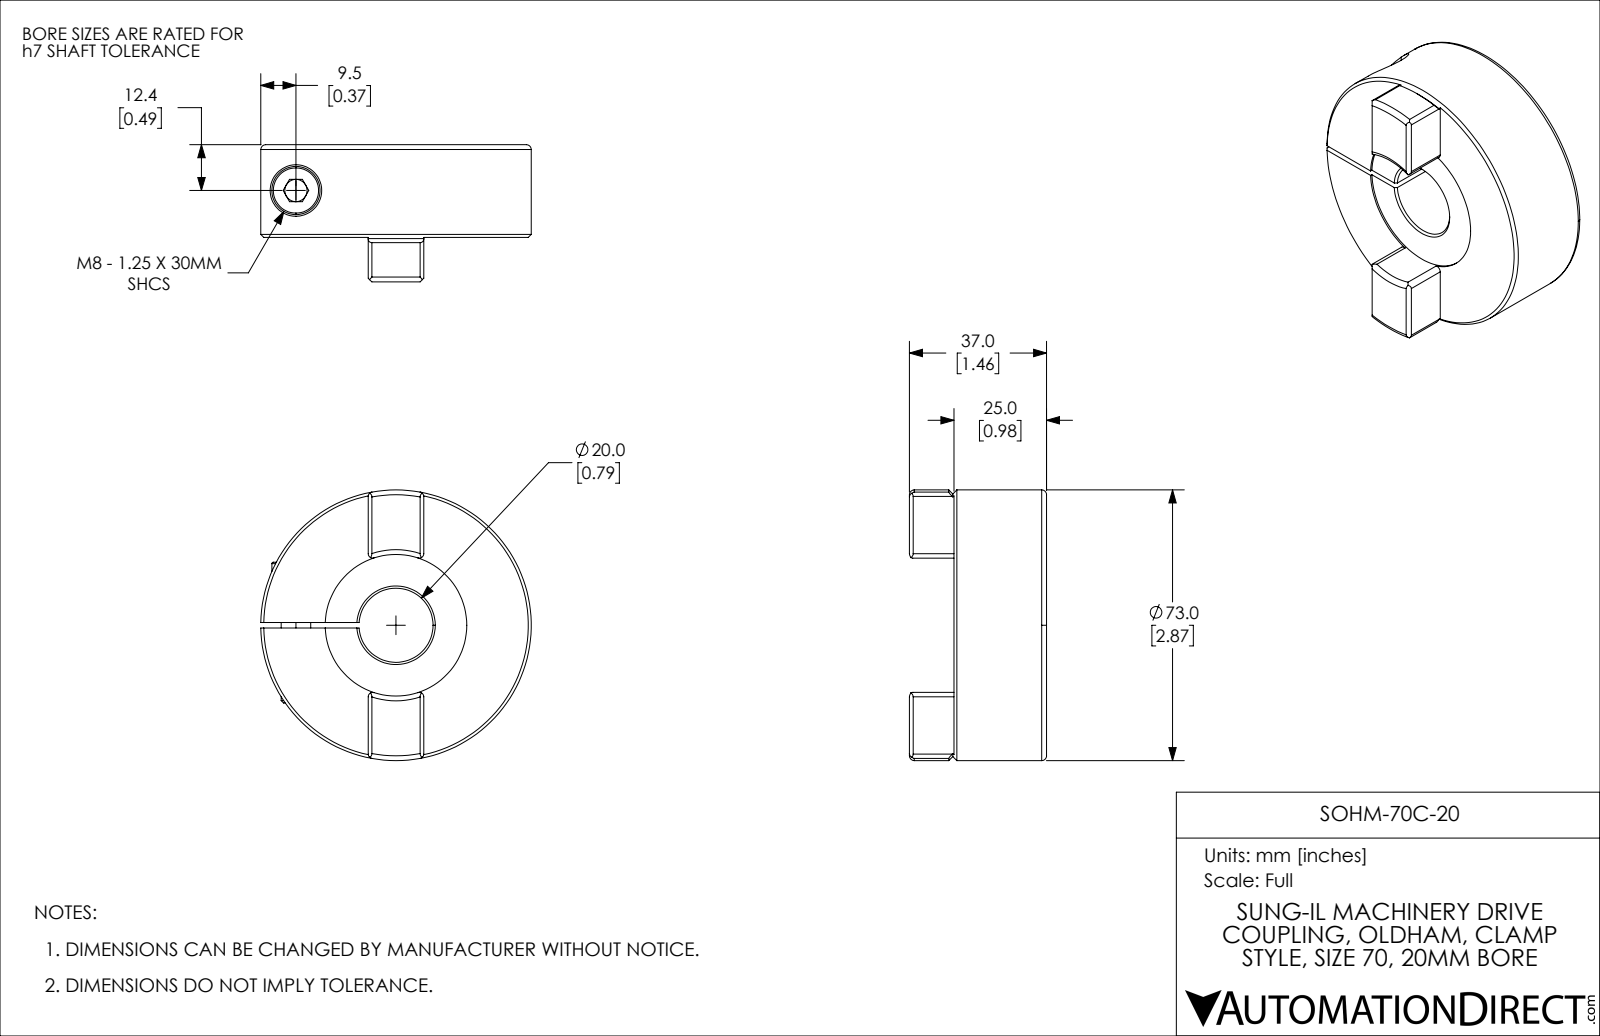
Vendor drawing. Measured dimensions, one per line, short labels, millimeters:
name: SOHM-70C-20
written by: SolidWorks 2021 (CONFIG_CONTROL_DESIGN)
unit: mm
bodies: 2 solids, 90 faces (35 planar, 30 cylindrical, 25 other)
size: 73 × 72.99 × 37
volume: 99 960 mm³; area: 20 240 mm²
holes: 1× ⌀6, 1× ⌀6.8, 1× ⌀8.5, 1× ⌀13.9, 1× ⌀20, 1× ⌀38.2
bosses: 1× ⌀73, 1× ⌀13, 1× ⌀8
rounds: 8× R1.2, 1× R50
face distances: 25, 24.5, 0.5, 1.5, 37, 12.5, 12, 15, 9.75, 8.25
